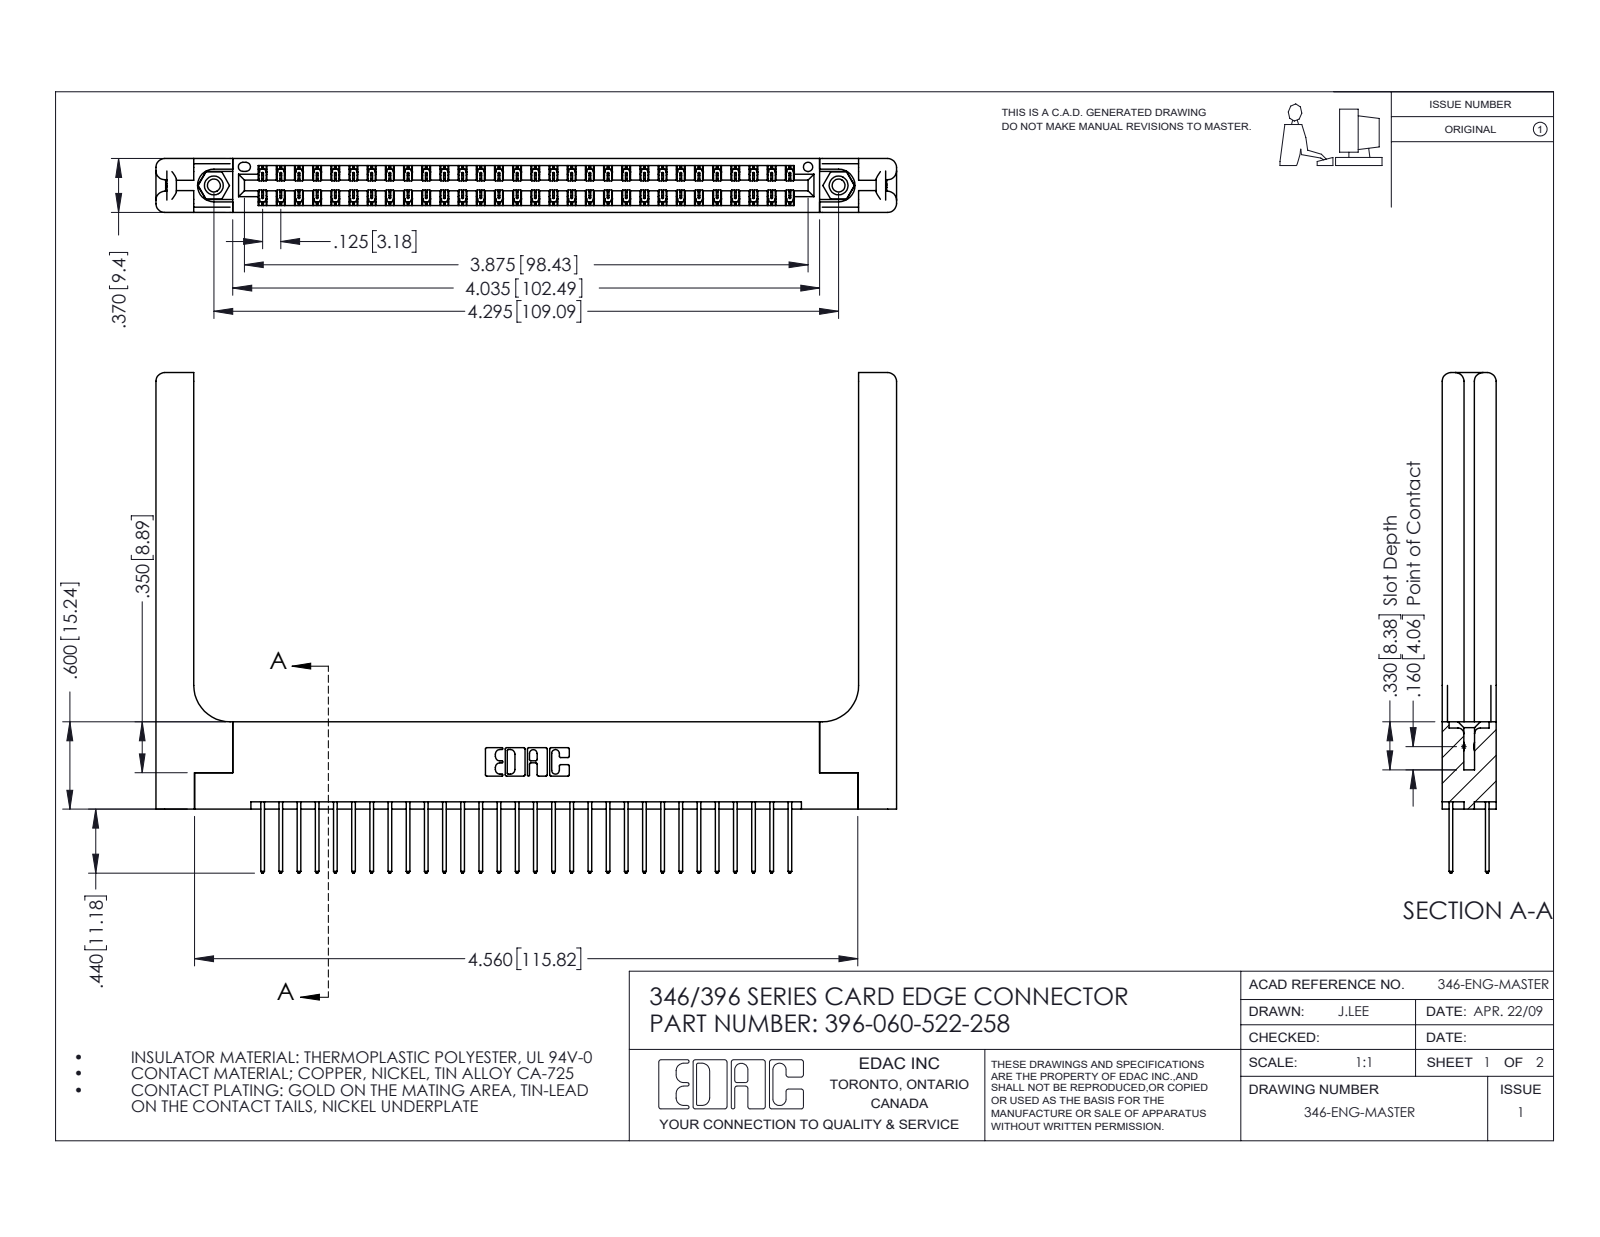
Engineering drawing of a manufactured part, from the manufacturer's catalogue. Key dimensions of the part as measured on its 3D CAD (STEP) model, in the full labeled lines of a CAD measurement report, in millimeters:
Part name (STEP PRODUCT): 345-250-001_345-250-001-102; 345-292-001_345-293-122; 346-220-058_345-220-058; 346 Part_Flush Mounting Lugs - 0.156 Dia-TH (+1 more)
STEP written by: SolidWorks 2016 (CONFIG_CONTROL_DESIGN)
Units: millimetres
Bodies: 65 solids, 3498 faces (2324 planar, 1114 cylindrical, 60 other)
Overall size (bounding box): 129.3 × 87.4 × 9.4
Volume: 20 160 mm³ · Surface area: 22 910 mm²
Round holes (diameter × count): ⌀2.3 ×2, ⌀3.2 ×2, ⌀4 ×2, ⌀1.6 ×1
Round bosses / shafts (diameter × count): ⌀3.9 ×2
Partial cylindrical surfaces — rounded edges, fillets, slot ends (radius × count): R0.2 ×90, R0.3 ×60, R0.3 ×22, R1.5 ×16, R0.2 ×6, R0.8 ×6, R0.7 ×3, R0.4 ×2
Main face-to-face distances: 9.4, 1.2, 8.2, 1.8, 6.4, 3.8, 3.8, 0.6, 7.6, 7
Hole centre spacings: 6.2, 103.8, 109.1
